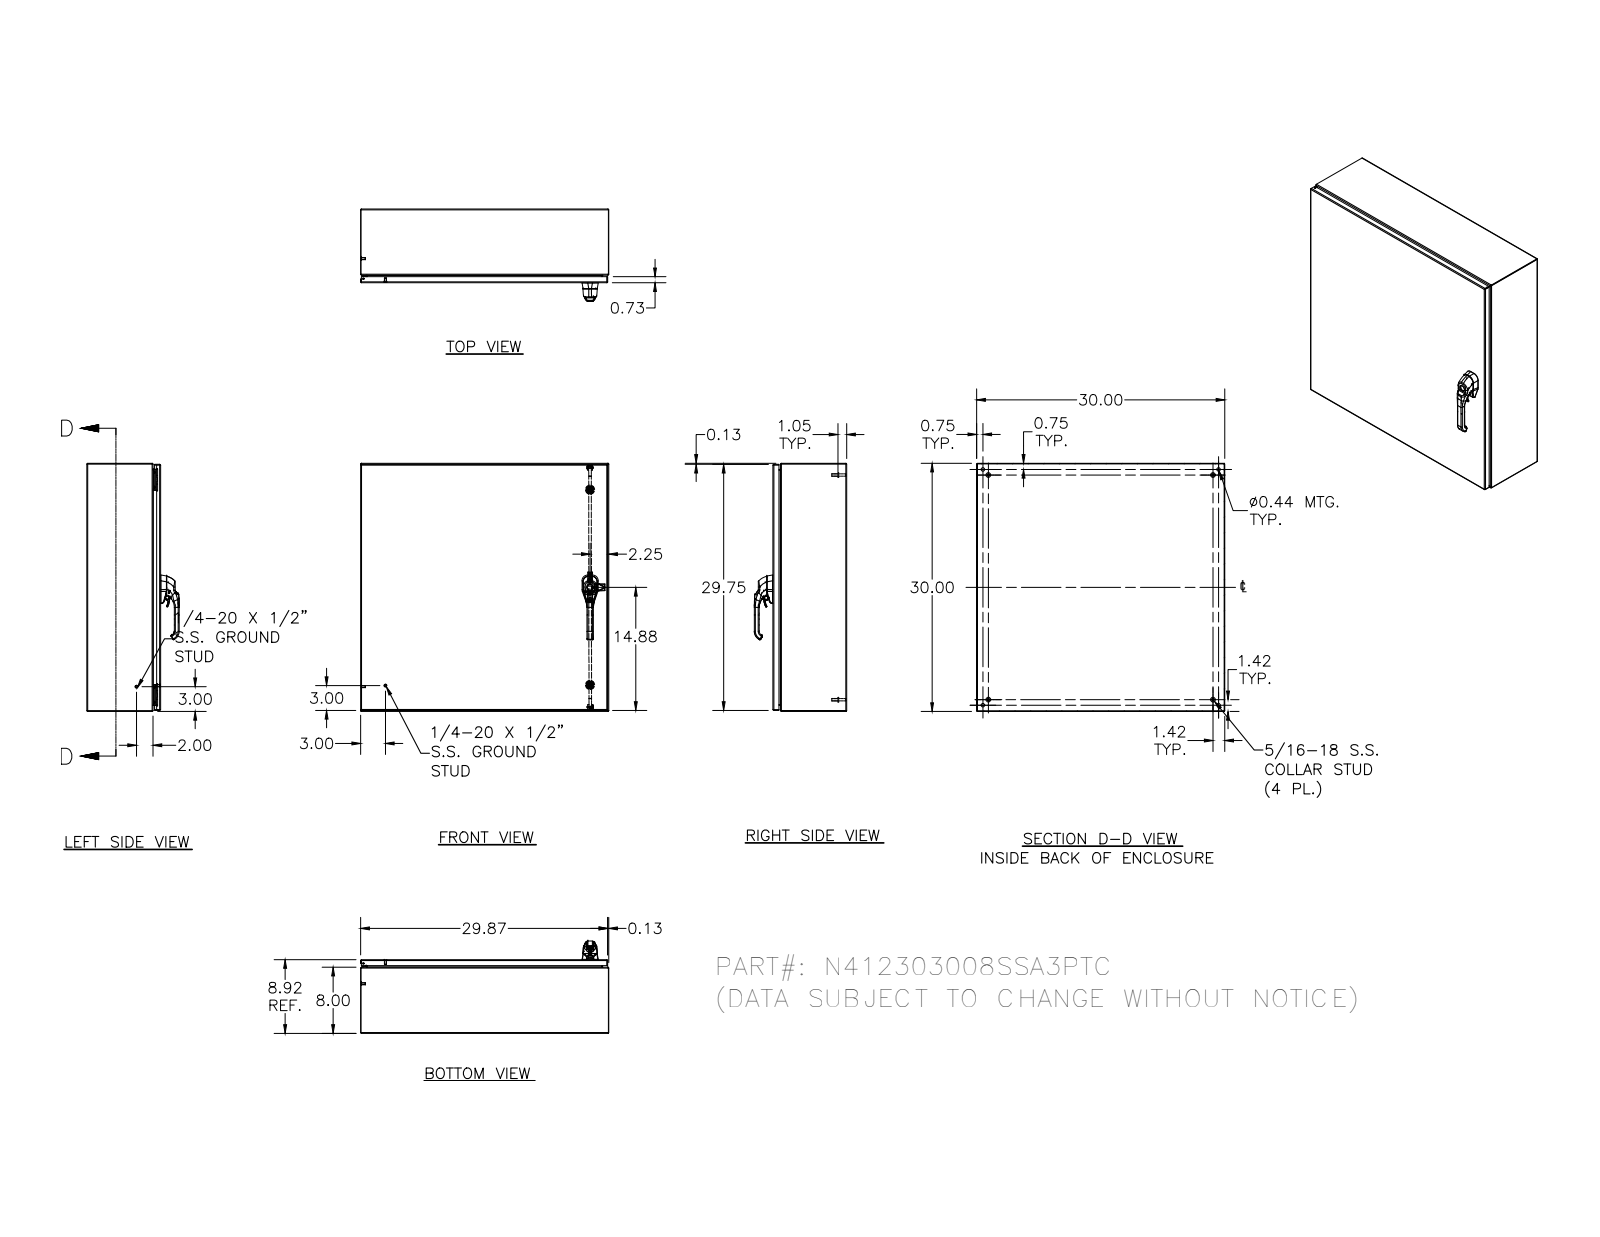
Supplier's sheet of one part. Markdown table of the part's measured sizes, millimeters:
| quantity | value |
| --- | --- |
| part name | N412303008SSA3PTC; N412303008SSA3PTCBKP; N4123030SSA3PTCLID; HFW328176 (+8 more) |
| STEP written by | Autodesk Inventor 2011 (AUTOMOTIVE_DESIGN) |
| units | millimeters |
| bodies | 63 solids, 3088 faces (1046 planar, 1119 cylindrical, 923 other) |
| overall size | 762 × 762 × 283.6 |
| volume | 3 812 000 mm³ |
| surface area | 3 975 000 mm² |
| round holes (diameter × count) | 4.2 × 6, 4.8 × 5, 2.4 × 4, 3.9 × 4, 4.2 × 4, 4.4 × 4, 5 × 4, 11.1 × 4, 5.4 × 3, 2.7 × 2, 4 × 2, 4.1 × 2 |
| round bosses / shafts (diameter × count) | 6.4 × 10, 6 × 6, 15 × 5, 14.3 × 4, 9.1 × 4, 8.1 × 4, 7.9 × 4, 7.6 × 4 |
| partial cylindrical surfaces (radius × count) | 0.5 × 188, 0.3 × 100, 0.8 × 30, 1.3 × 26, 0.5 × 23, 3 × 23, 2.7 × 20, 0.4 × 18 |
| main face-to-face distances | 1.9, 224.6, 760.1, 226.5, 222.7, 758.2, 762, 201.3, 23.3, 18.8 |
| hole center spacings | 660.3, 695.8, 723.9, 0.4, 16.8, 41.1, 677.1, 0.5 |
